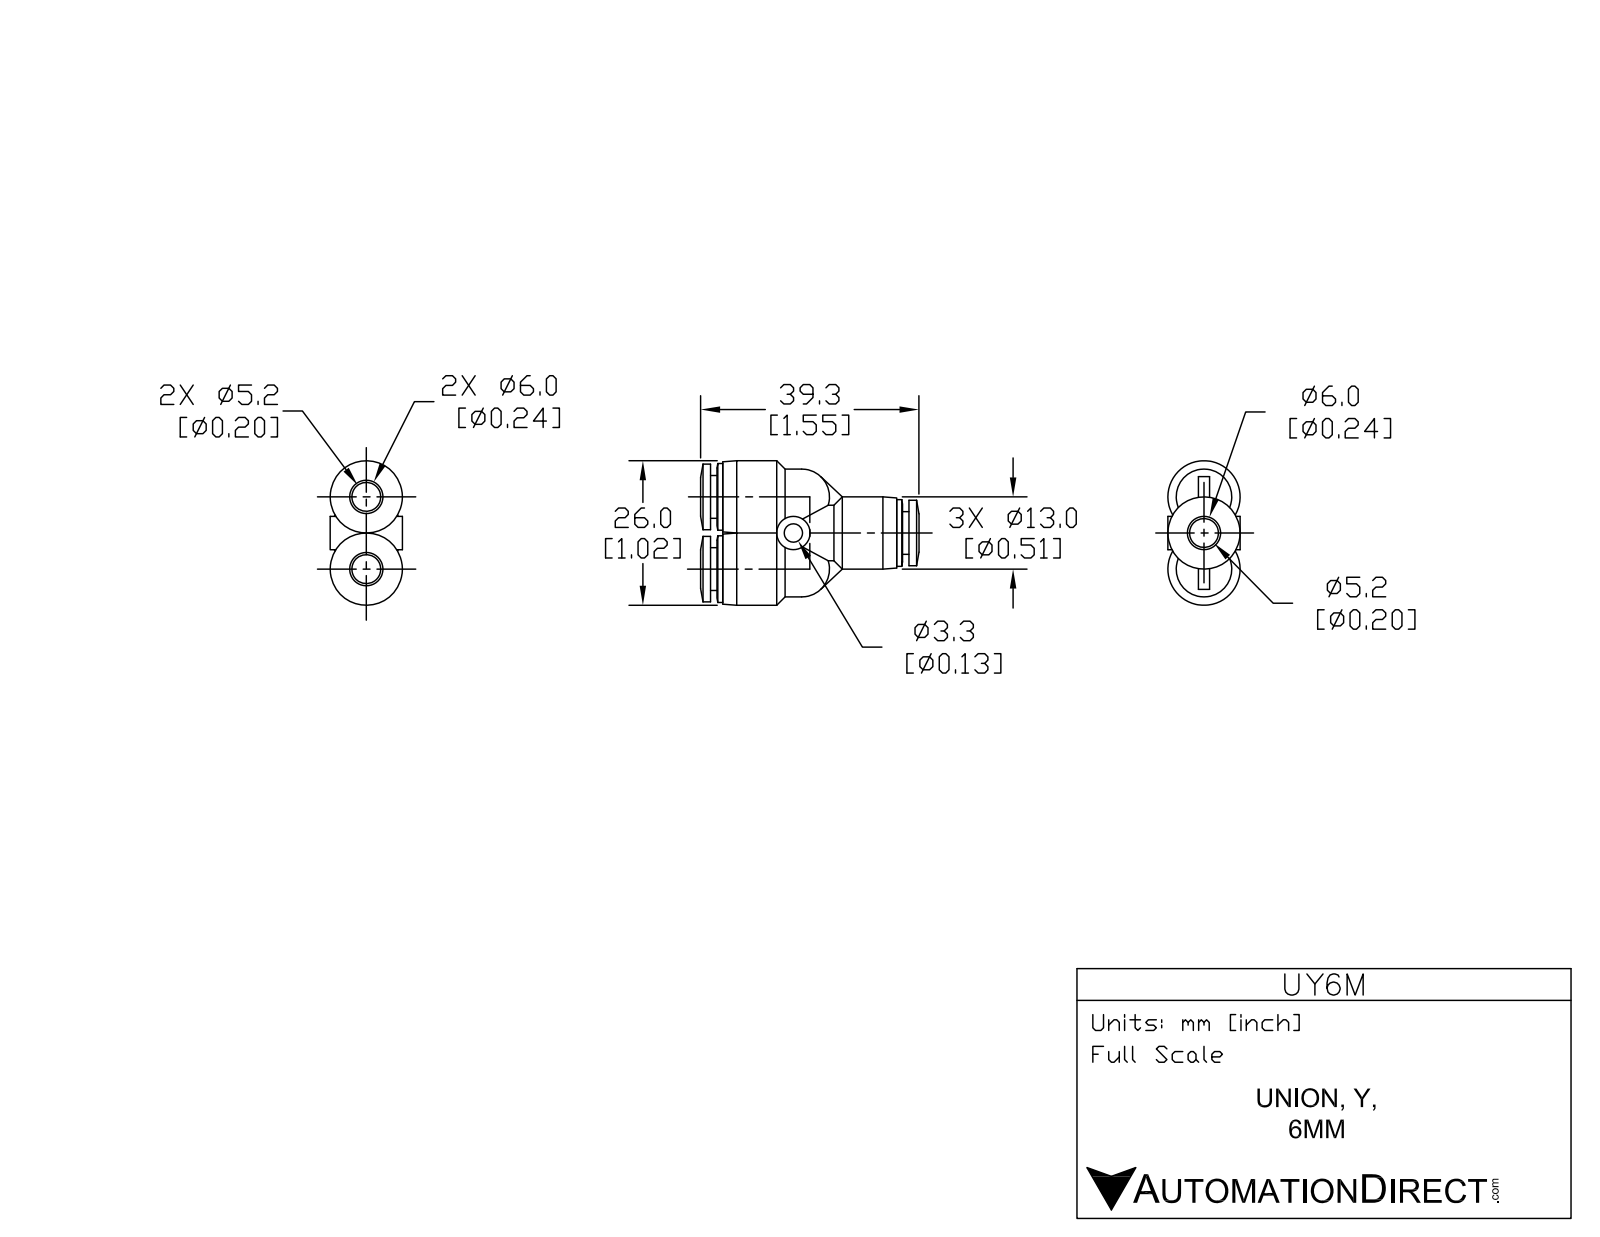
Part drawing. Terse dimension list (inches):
name: UY6M
written by: SolidWorks 2015 (AUTOMOTIVE_DESIGN)
unit: in
bodies: 1 solid, 107 faces (25 planar, 41 cylindrical, 41 other)
size: 1.543 × 1.024 × 0.512
volume: 0.309 in³; area: 6.795 in²
holes: 3× ⌀0.248, 1× ⌀0.13
bosses: 3× ⌀0.512, 3× ⌀0.472, 3× ⌀0.465, 3× ⌀0.303, 1× ⌀0.394, 1× ⌀0.236
rounds: 2× R0.197
face distances: 0.045, 1.356, 1.402, 1.311, 0.693, 0.087, 1.315, 0.041, 1.27, 0.622
hole spacings: 0.256, 0.512
